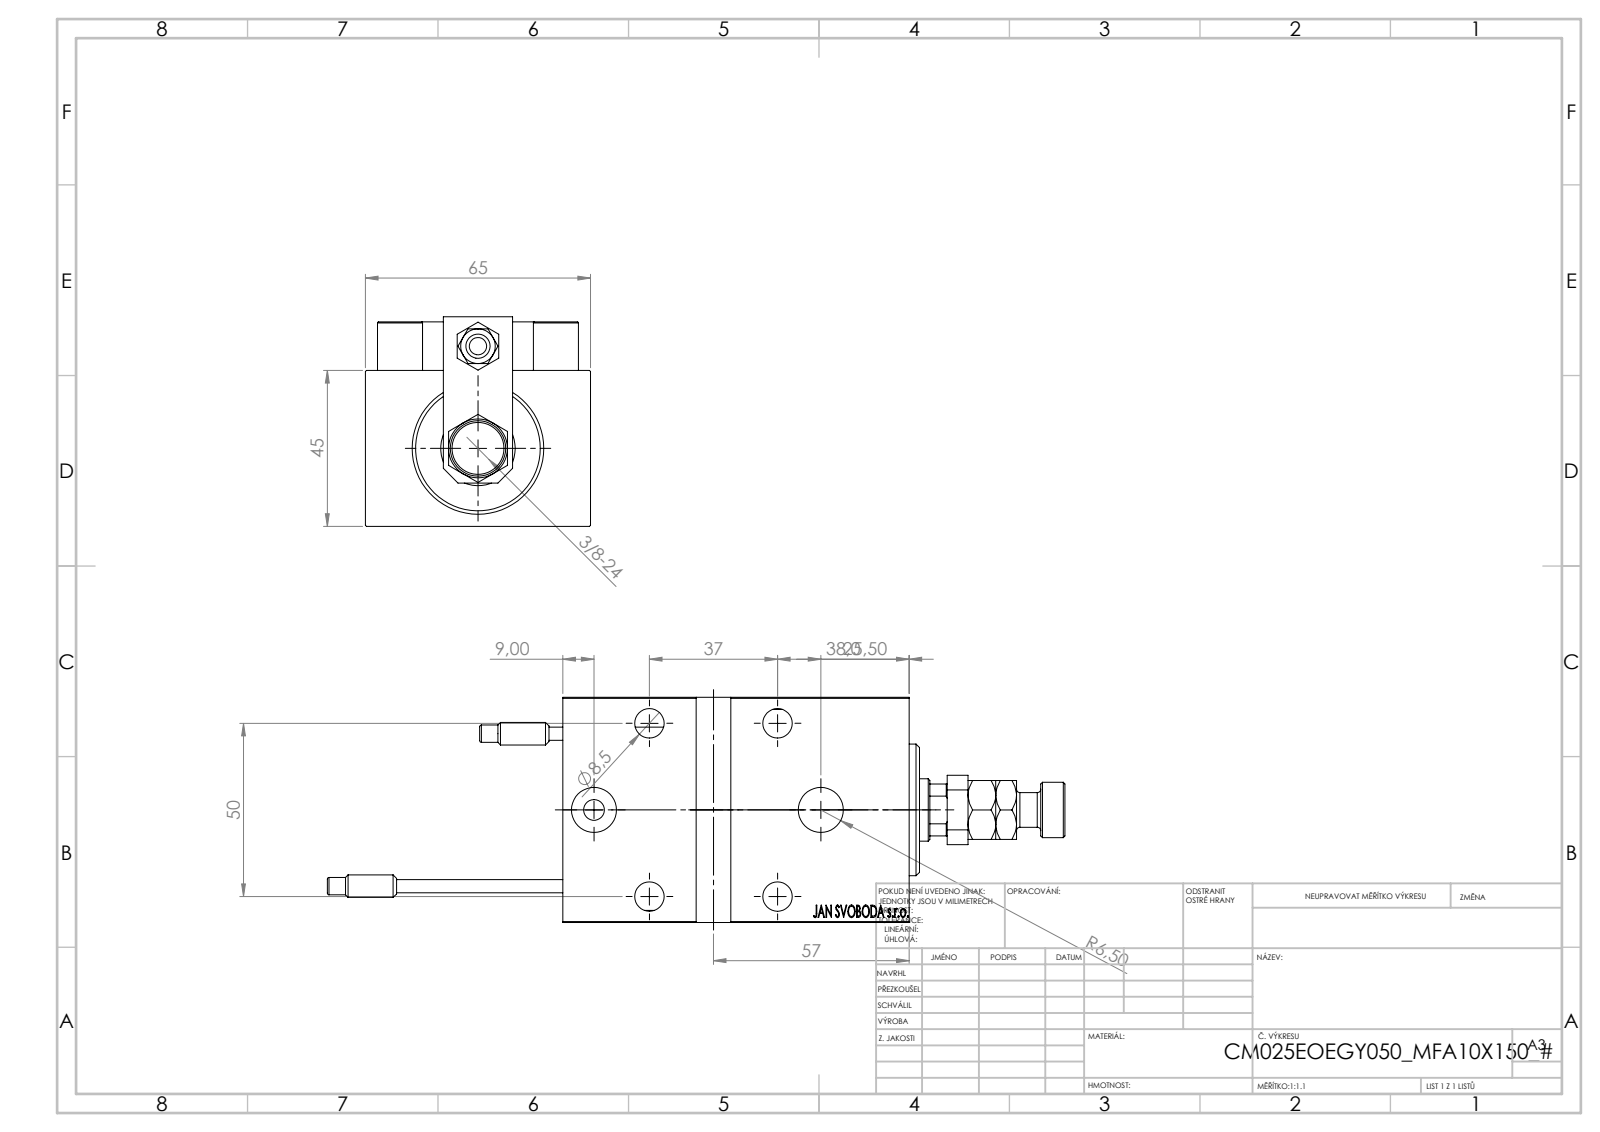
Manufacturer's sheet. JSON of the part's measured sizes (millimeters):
{"part_name": "SWITCH X; ALLEN BOLT D5; MAGNET; ZARAZKA (+8 more)", "step_written_by": "SolidWorks 2019 (CONFIG_CONTROL_DESIGN)", "units": "millimeters", "bodies": {"solids": 25, "faces": 1360, "planar": 587, "cylindrical": 188, "other": 585}, "overall_size": [213, 65, 60.5], "volume_mm3": 324268, "surface_area_mm2": 80475, "round_holes": [[8, 5], [8.5, 5], [3.2, 4], [4, 4], [13.5, 4], [5, 2], [13, 2], [7, 1], [14.5, 1], [18, 1], [21.5, 1], [25, 1]], "round_bosses_or_shafts": [[5, 4], [6.5, 2], [3.8, 2], [38, 1], [27, 1], [16, 1], [13, 1], [11, 1]], "partial_cylinders_radius": [[0.3, 30], [3, 2], [8.5, 1]], "face_to_face_distances": [45, 65, 14, 59, 6, 100, 111, 13, 10, 5], "hole_center_spacings": [40.31, 10.77, 11.37, 20, 21.03, 25, 27.95, 29.59]}
